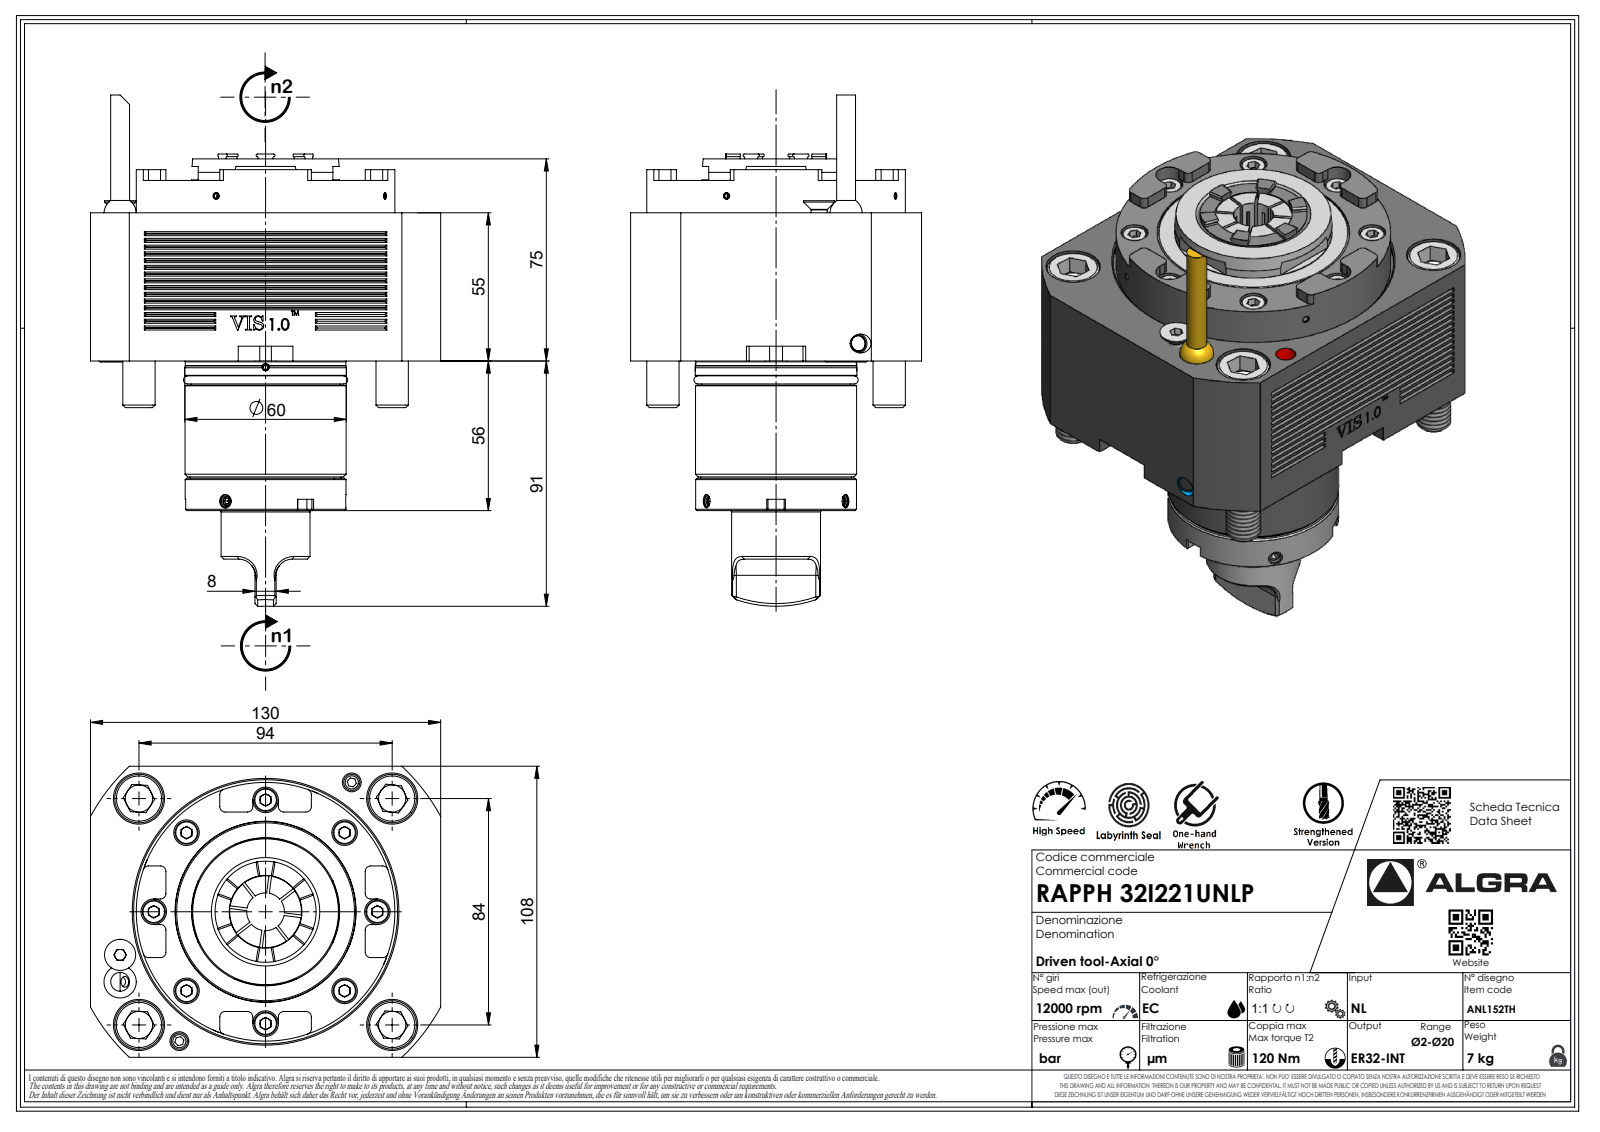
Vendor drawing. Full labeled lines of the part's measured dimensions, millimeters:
Part name (STEP PRODUCT): RAPPH32I221UNLP
STEP written by: SolidWorks 2023 (AUTOMOTIVE_DESIGN)
Units: millimetres
Bodies: 1 solid, 572 faces (333 planar, 104 cylindrical, 135 other)
Overall size (bounding box): 189.7 × 130 × 108
Volume: 1 029 000 mm³ · Surface area: 78 916 mm²
Round holes (diameter × count): ⌀1.8 ×1, ⌀2.1 ×1, ⌀4 ×1
Round bosses / shafts (diameter × count): ⌀12 ×4, ⌀96 ×1, ⌀60 ×1, ⌀59.8 ×1, ⌀59.7 ×1, ⌀59.6 ×1, ⌀55.2 ×1, ⌀55 ×1
Partial cylindrical surfaces — rounded edges, fillets, slot ends (radius × count): R2 ×25, R8 ×8, R0.33 ×7, R0.52 ×7, R3.7 ×7, R6 ×6, R4.75 ×4, R3 ×3
Main face-to-face distances: 55, 108, 12, 67, 130, 110.5, 20, 8, 75, 4
